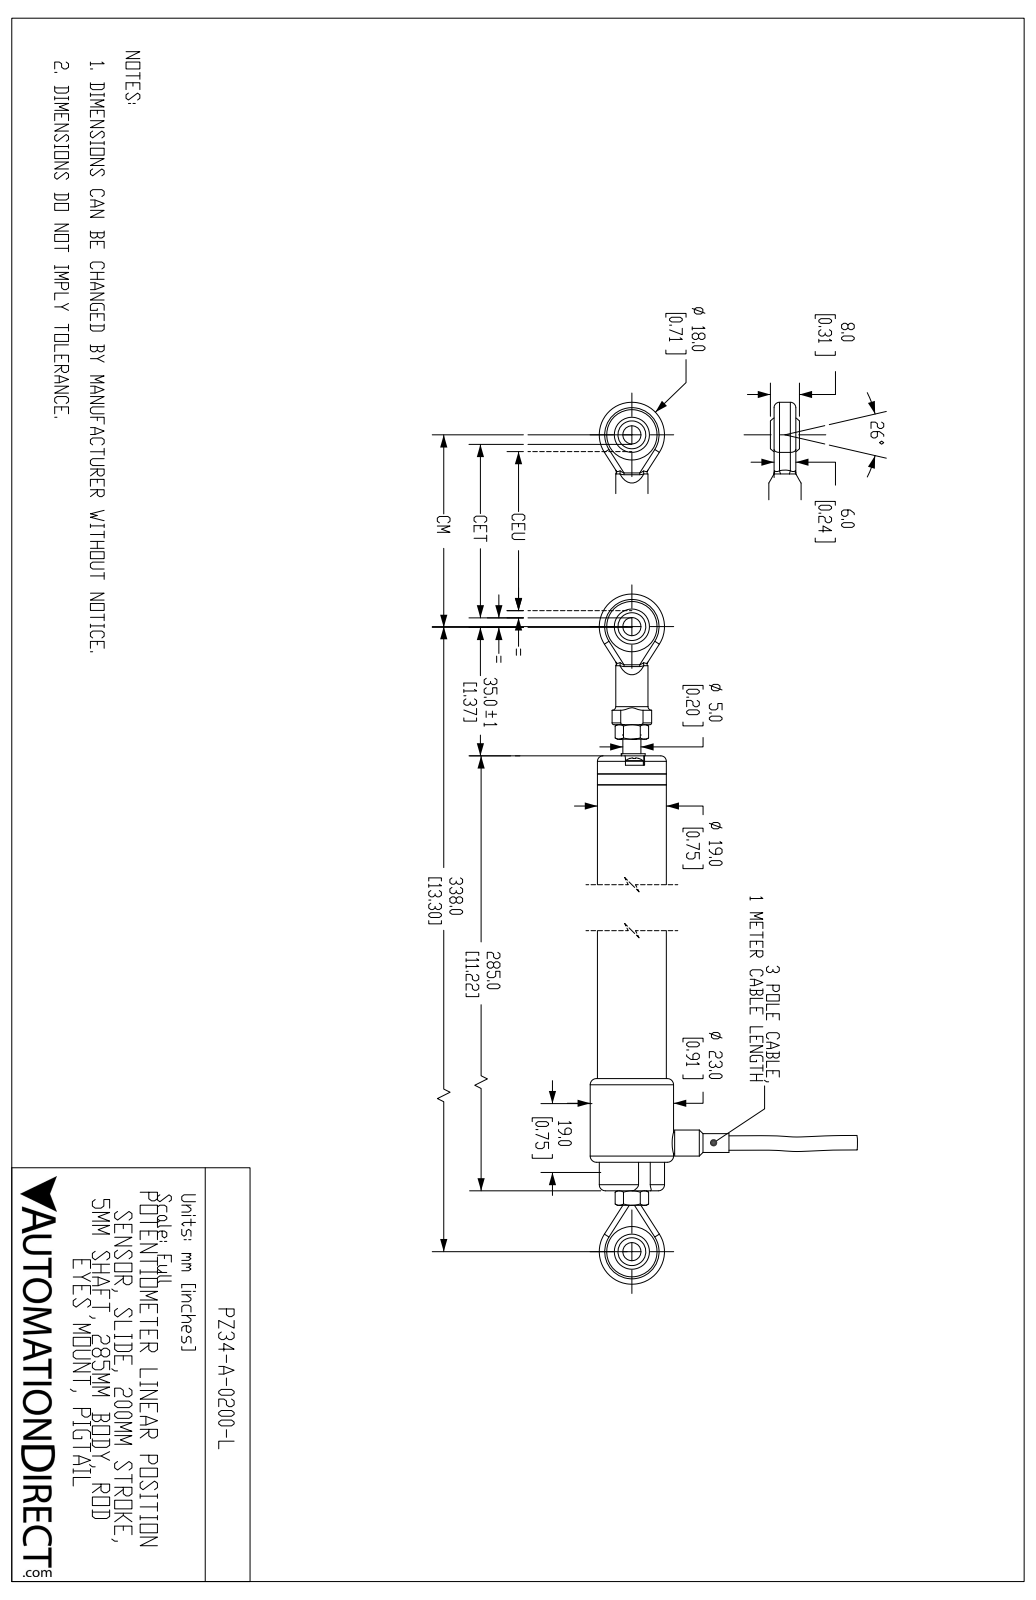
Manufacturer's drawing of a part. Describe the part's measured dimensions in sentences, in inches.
The part is named "PZ34-A-0200-L". Its 3-D file was written by "SolidWorks 2019 (AUTOMOTIVE_DESIGN)". It is 18 solids with 916 faces: 334 planar, 198 cylindrical and 384 other. Overall it measures 13.996 by 2.904 by 0.906 inches. Its volume is 5.82 cubic inches and its surface area 52.6 square inches. Round holes: 4 of diameter 0.079, 4 of diameter 0.114, 2 of diameter 0.197, 2 of diameter 0.209, 2 of diameter 0.547, 1 of diameter 0.138, 1 of diameter 0.165, 1 of diameter 0.24, 1 of diameter 0.354, 1 of diameter 0.75. Round bosses or shafts: 5 of diameter 0.197, 4 of diameter 0.098, 1 of diameter 0.906, 1 of diameter 0.748, 1 of diameter 0.709, 1 of diameter 0.35, 1 of diameter 0.283, 1 of diameter 0.236. Partial cylindrical surfaces (rounded edges, fillets, slot ends): 8 of radius 0.059, 4 of radius 0.01, 2 of radius 0.02, 2 of radius 0.039, 2 of radius 0.104, 2 of radius 0.354, 1 of radius 0.017, 1 of radius 0.063. The main face-to-face distances are 10.315, 10.197, 0.118, 0.315, 0.224, 0.213, 0.217, 0.051, 0.039, 0.264. The hole center spacings are 0.269, 0.082, 0.532, 0.539, 13.287.
